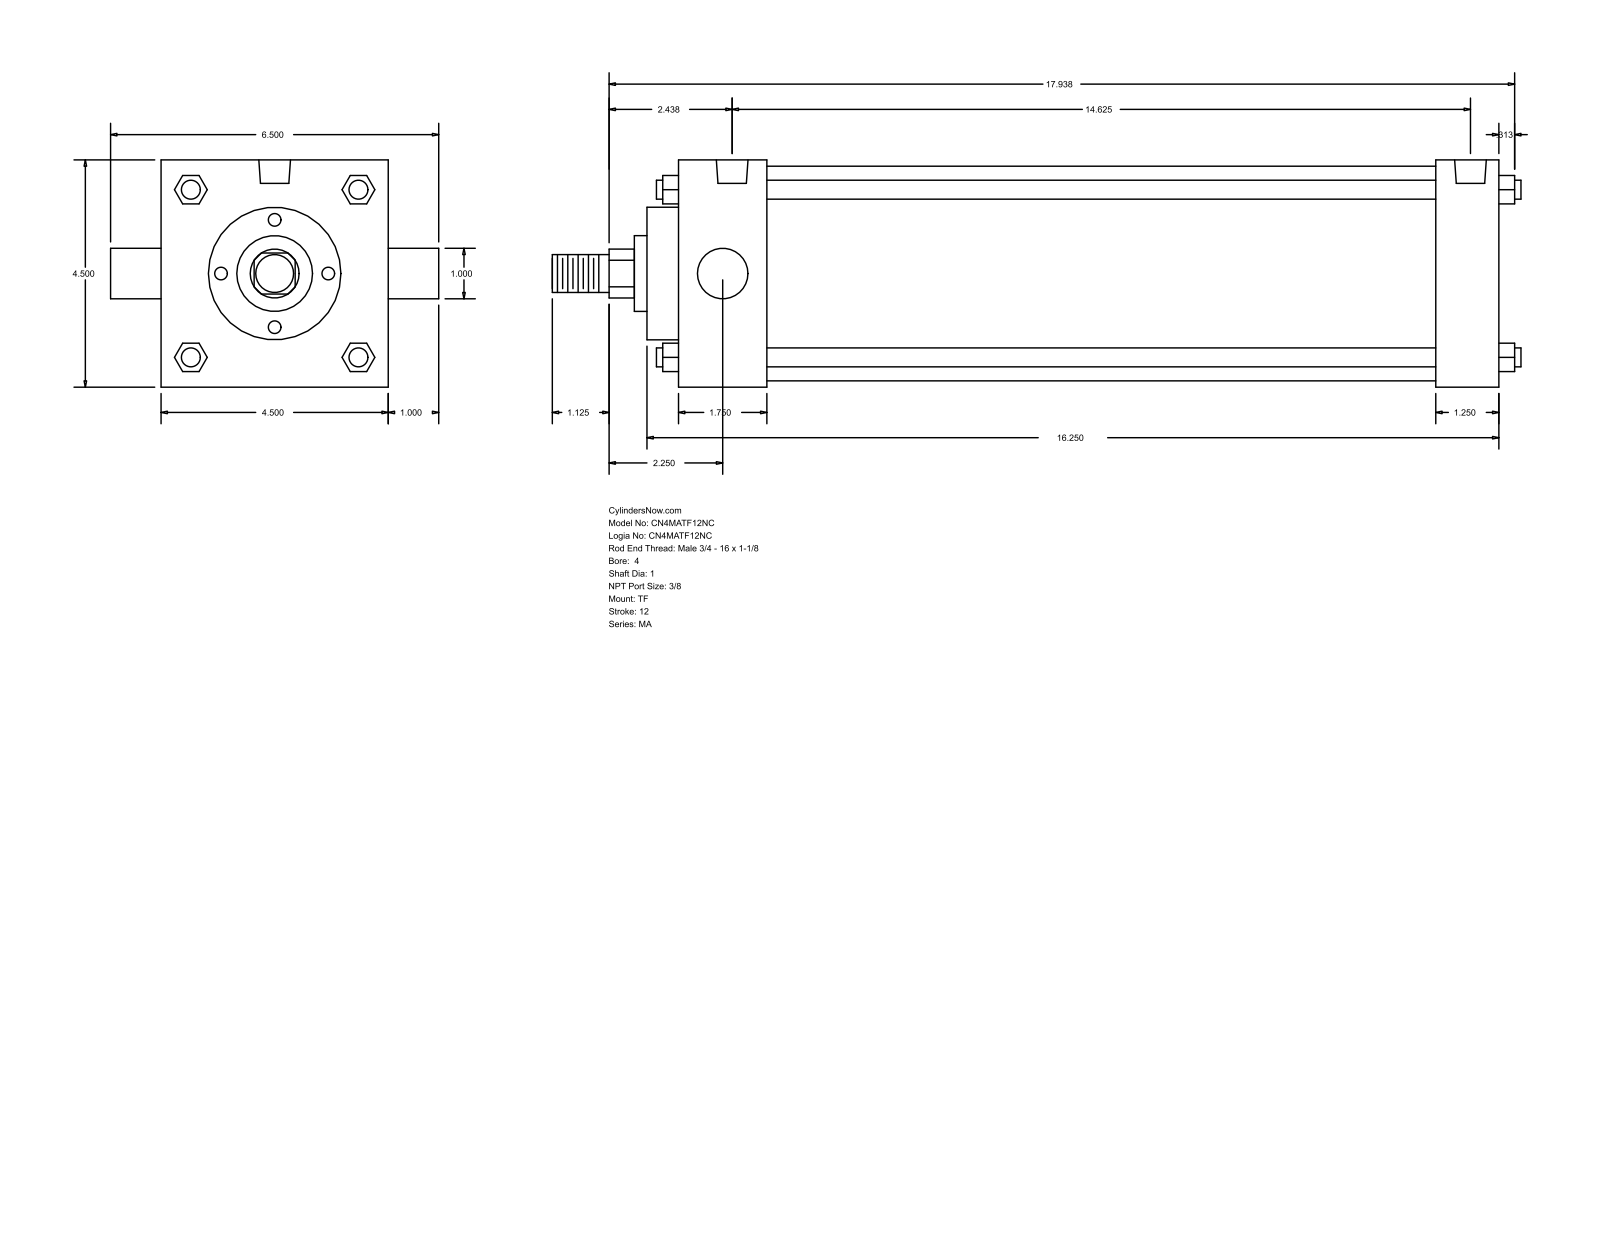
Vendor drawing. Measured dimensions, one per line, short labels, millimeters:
name: MA_TF__0400_1
written by: GSSL Pune (CONFIG_CONTROL_DESIGN)
unit: mm
bodies: 0 solids, 122 faces (93 planar, 29 cylindrical, 0 other)
size: 487.36 × 165.1 × 114.3
holes: 3× ⌀11.11, 2× ⌀15.93
bosses: 4× ⌀9.53, 2× ⌀25.4, 1× ⌀107.95, 1× ⌀66.67, 1× ⌀38.1, 1× ⌀19.05
rounds: 1× R12.29
face distances: 114.3, 412.76, 381.01, 31.75, 44.46, 336.55, 368.3, 15.87, 60.33, 396.88
hole spacings: 4.76, 4.77, 361.95, 366.71, 366.72, 371.48
